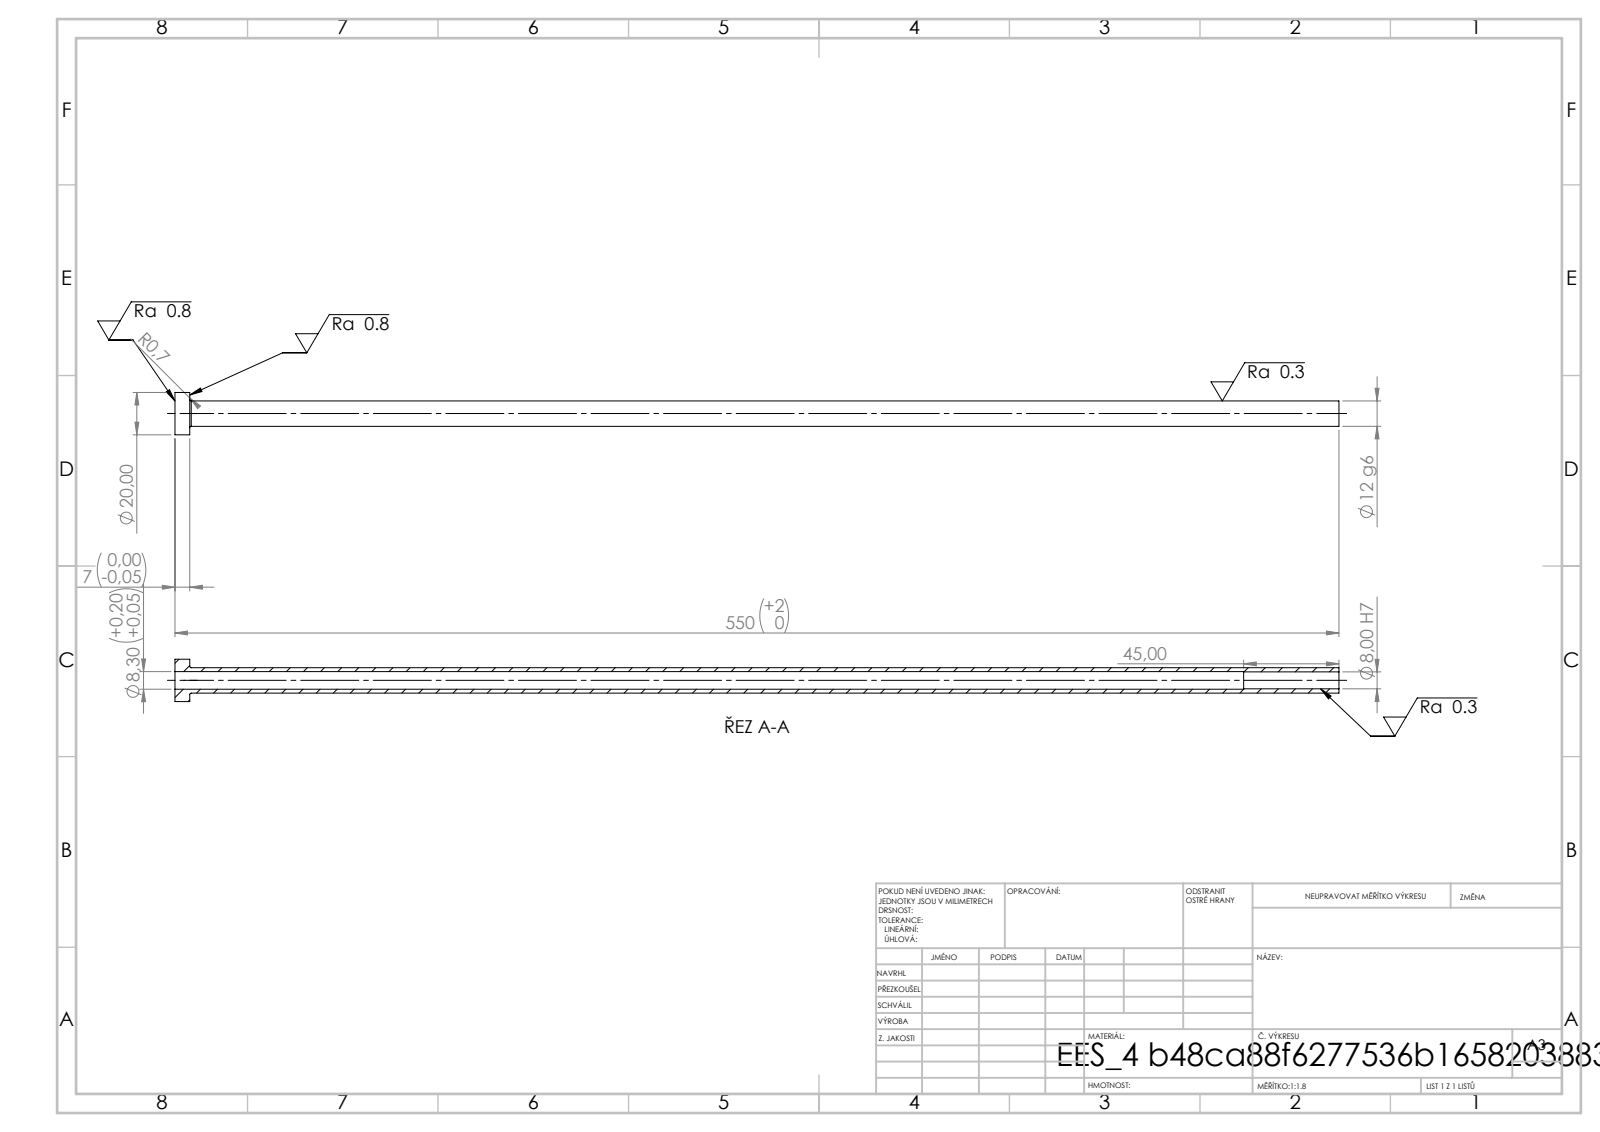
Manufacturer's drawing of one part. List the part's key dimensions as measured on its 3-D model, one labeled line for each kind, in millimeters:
STEP written by: SolidWorks 2019 (CONFIG_CONTROL_DESIGN)
Units: millimetres
Bodies: 1 solid, 14 faces (4 planar, 8 cylindrical, 2 other)
Overall size (bounding box): 550 × 20 × 20
Volume: 34 030 mm³ · Surface area: 35 726 mm²
Round holes (diameter × count): ⌀8 ×1, ⌀8.3 ×1
Round bosses / shafts (diameter × count): ⌀20 ×1, ⌀12 ×1
Main face-to-face distances: 7, 550, 543, 505, 498, 45
